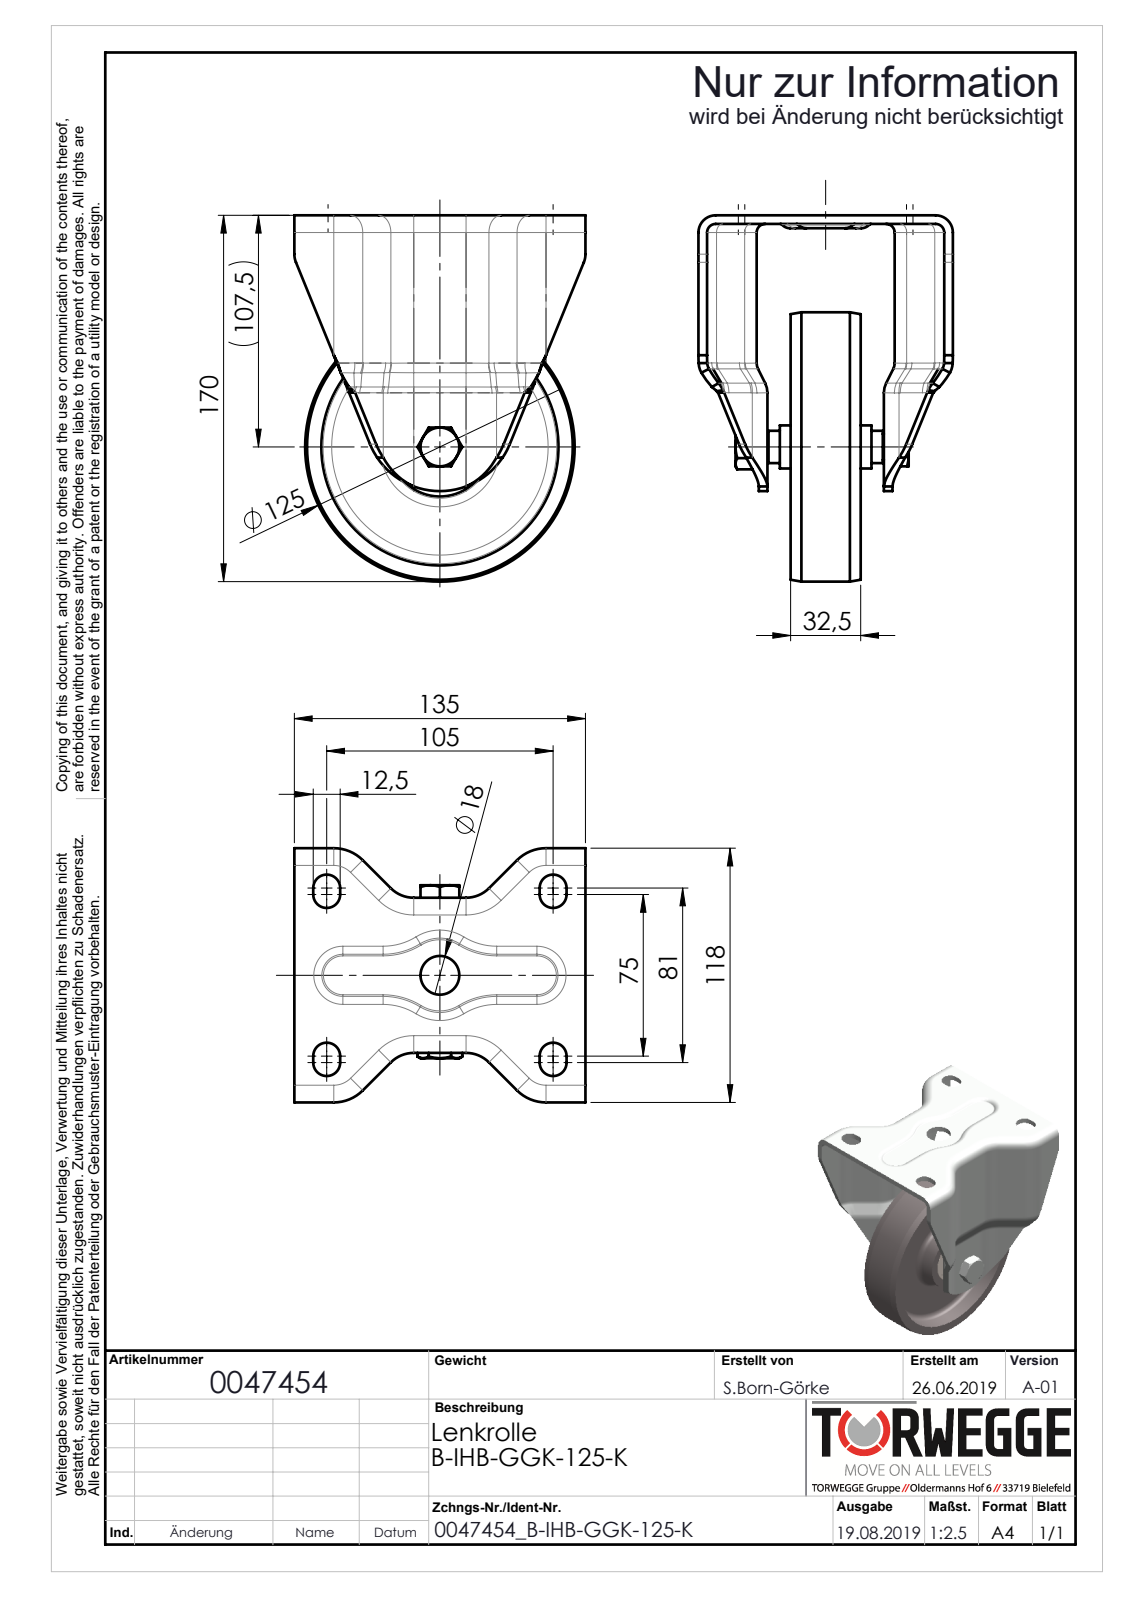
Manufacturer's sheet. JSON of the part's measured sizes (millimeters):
{"part_name": "0047454_B-IHB-GGK-125-K_(A-01)", "step_written_by": "SolidWorks 2018 (AUTOMOTIVE_DESIGN)", "units": "millimeters", "bodies": {"solids": 17, "faces": 628, "planar": 142, "cylindrical": 196, "other": 290}, "overall_size": [170, 135, 118], "volume_mm3": 358863, "surface_area_mm2": 156497, "round_holes": [[10.2, 1], [12, 1], [12.5, 1], [15, 1], [15.5, 1], [18, 1], [20.3, 1], [28.48, 1], [29.7, 1], [30, 1], [35, 1]], "round_bosses_or_shafts": [[125, 1], [21.52, 1], [20, 1], [18, 1]], "partial_cylinders_radius": [[10, 18], [6, 12], [4, 8], [6.25, 8], [8, 8], [15, 8], [19, 8], [1, 4]], "face_to_face_distances": [4, 13, 19.5, 2, 5, 6.5, 23, 91, 20.96, 28]}
